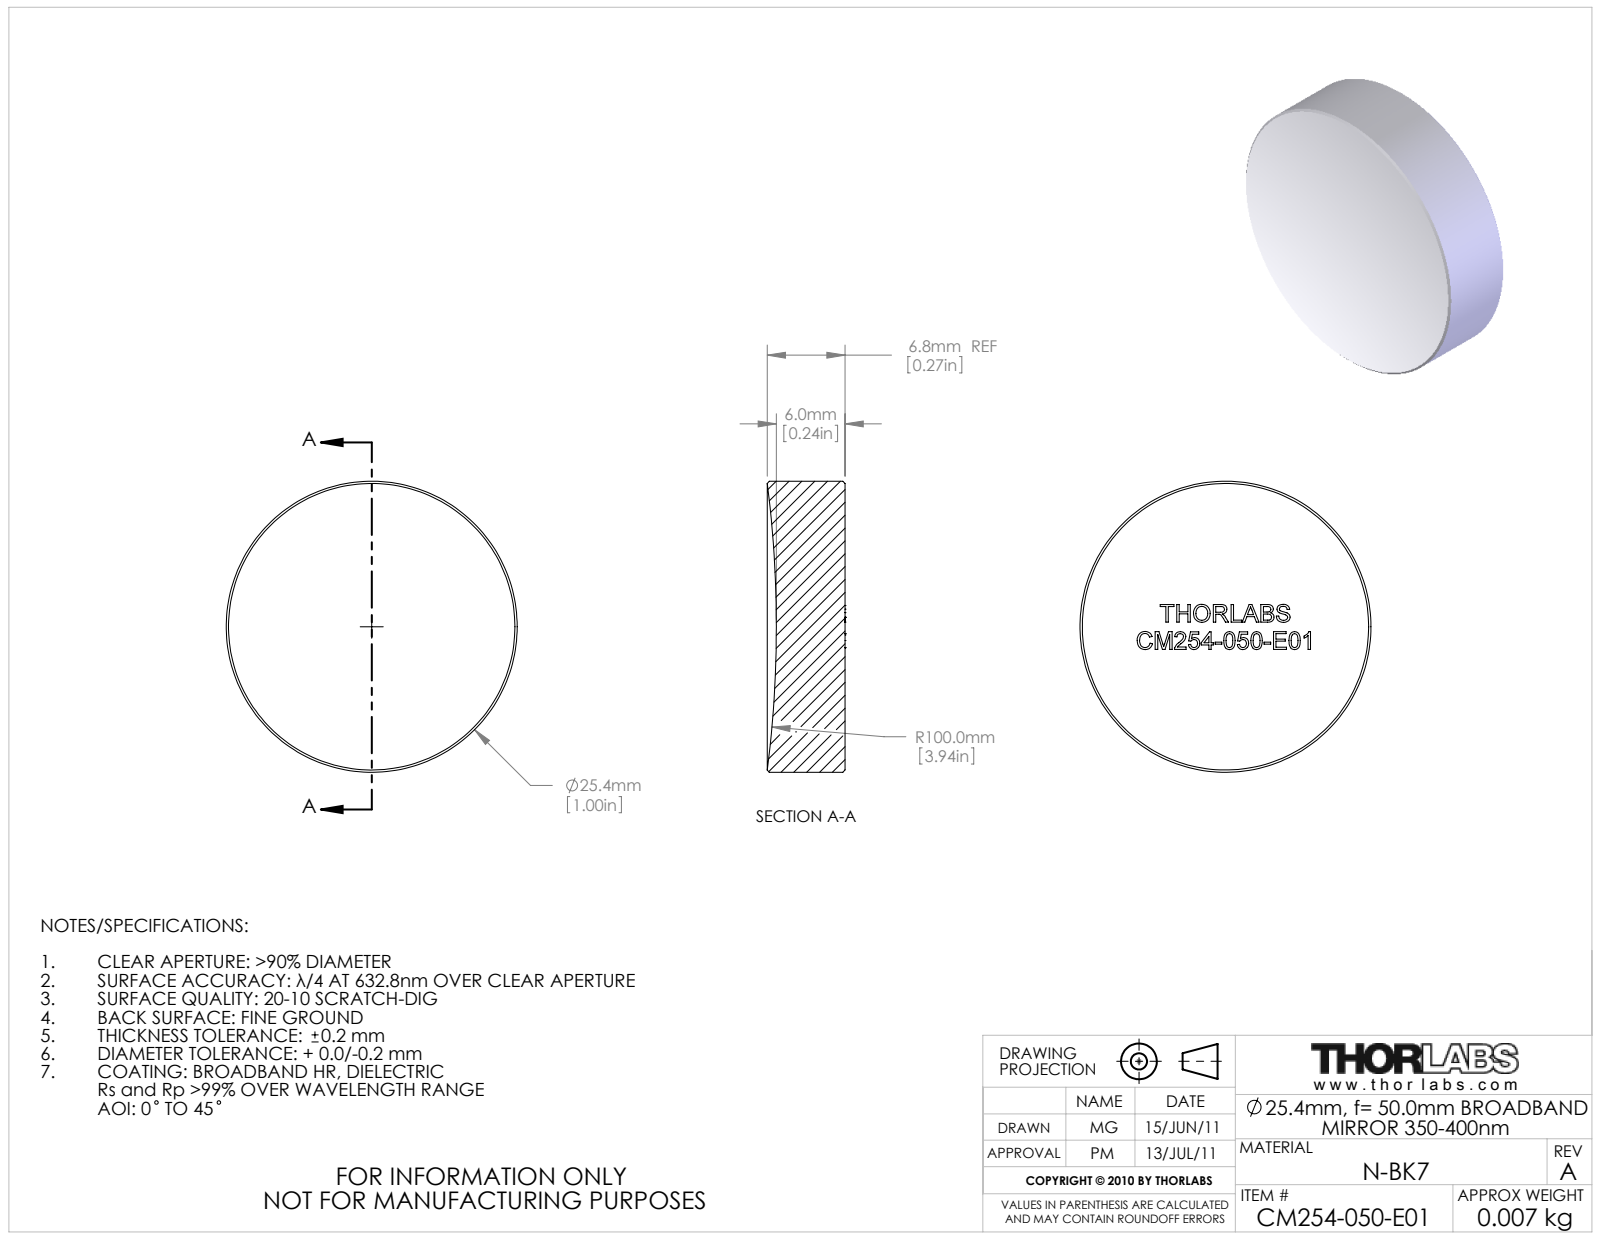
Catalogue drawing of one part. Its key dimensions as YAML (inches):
part_name: "22612-E0W"
step_written_by: "SolidWorks 2011 (AUTOMOTIVE_DESIGN)"
units: inches
bodies: {solids: 0, faces: 45, planar: 33, cylindrical: 2, other: 10}
overall_size: [1, 1, 0.267]
round_bosses_or_shafts:
  - {diameter: 1, count: 1}
